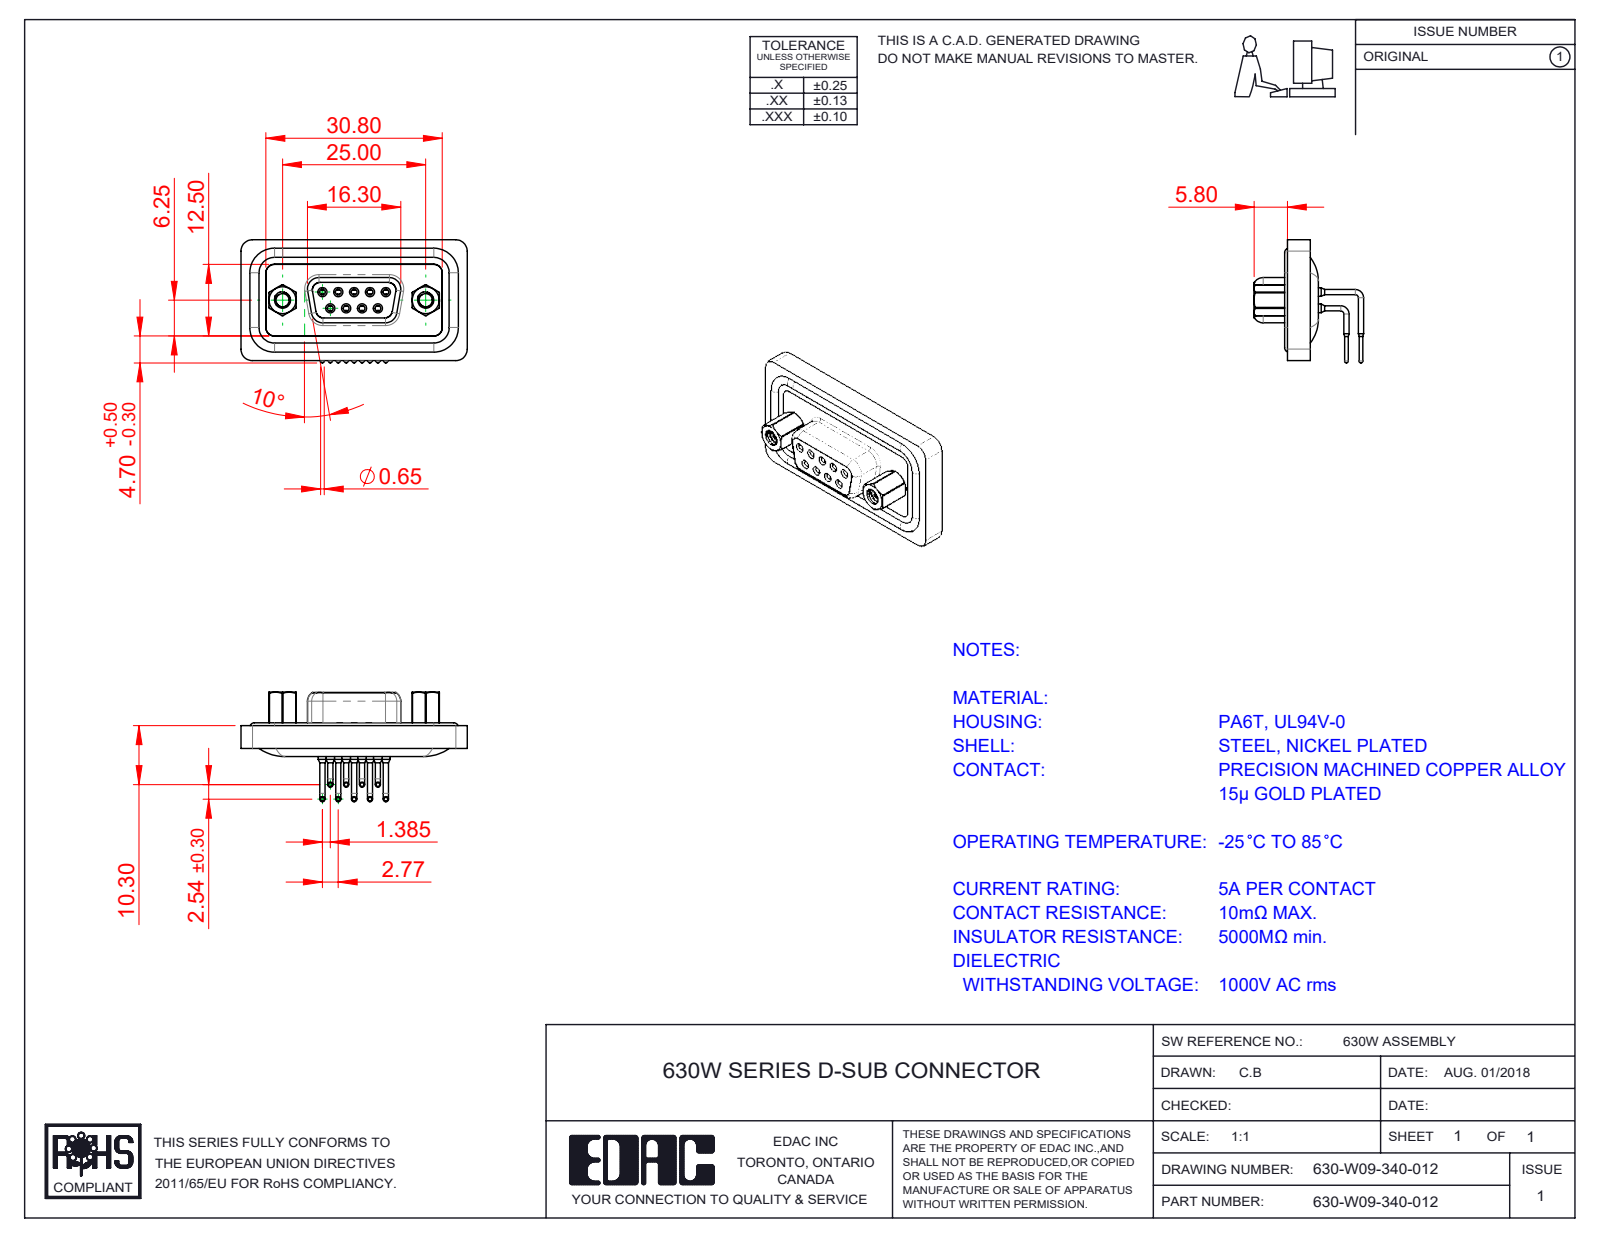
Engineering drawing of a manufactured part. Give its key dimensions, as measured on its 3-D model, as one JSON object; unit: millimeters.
{"part_name": "630W 4-40 Threaded Rivet_Stabilizer; 630W Housing_09 Contacts; 630W Contact Row 1; 630W Shell_09 Contacts (+4 more)", "step_written_by": "SolidWorks 2023 (CONFIG_CONTROL_DESIGN)", "units": "millimeters", "bodies": {"solids": 17, "faces": 912, "planar": 236, "cylindrical": 441, "other": 235}, "overall_size": [39.51, 21.5, 19.59], "volume_mm3": 4396, "surface_area_mm2": 7397, "round_holes": [[1, 9], [1.1, 9], [1.5, 9], [1.7, 9], [1.8, 9], [2, 9], [2.26, 2], [2.29, 2], [4, 2], [4.8, 2], [5, 2]], "round_bosses_or_shafts": [[0.9, 18], [1.6, 13], [0.65, 9], [1.5, 4], [4.9, 2], [2.79, 2], [5, 1]], "partial_cylinders_radius": [[1.5, 14], [2, 14], [1.35, 8], [2.7, 6], [0.5, 4], [0.9, 4], [1.6, 4], [1.75, 4]], "face_to_face_distances": [0.4, 1.6, 1.8, 1.1, 2.9, 2.5, 0.5, 4.3, 4, 0.7], "hole_center_spacings": [3.16, 2.77, 5.54, 5.03, 5.04, 7.48, 7.49, 8.31]}
